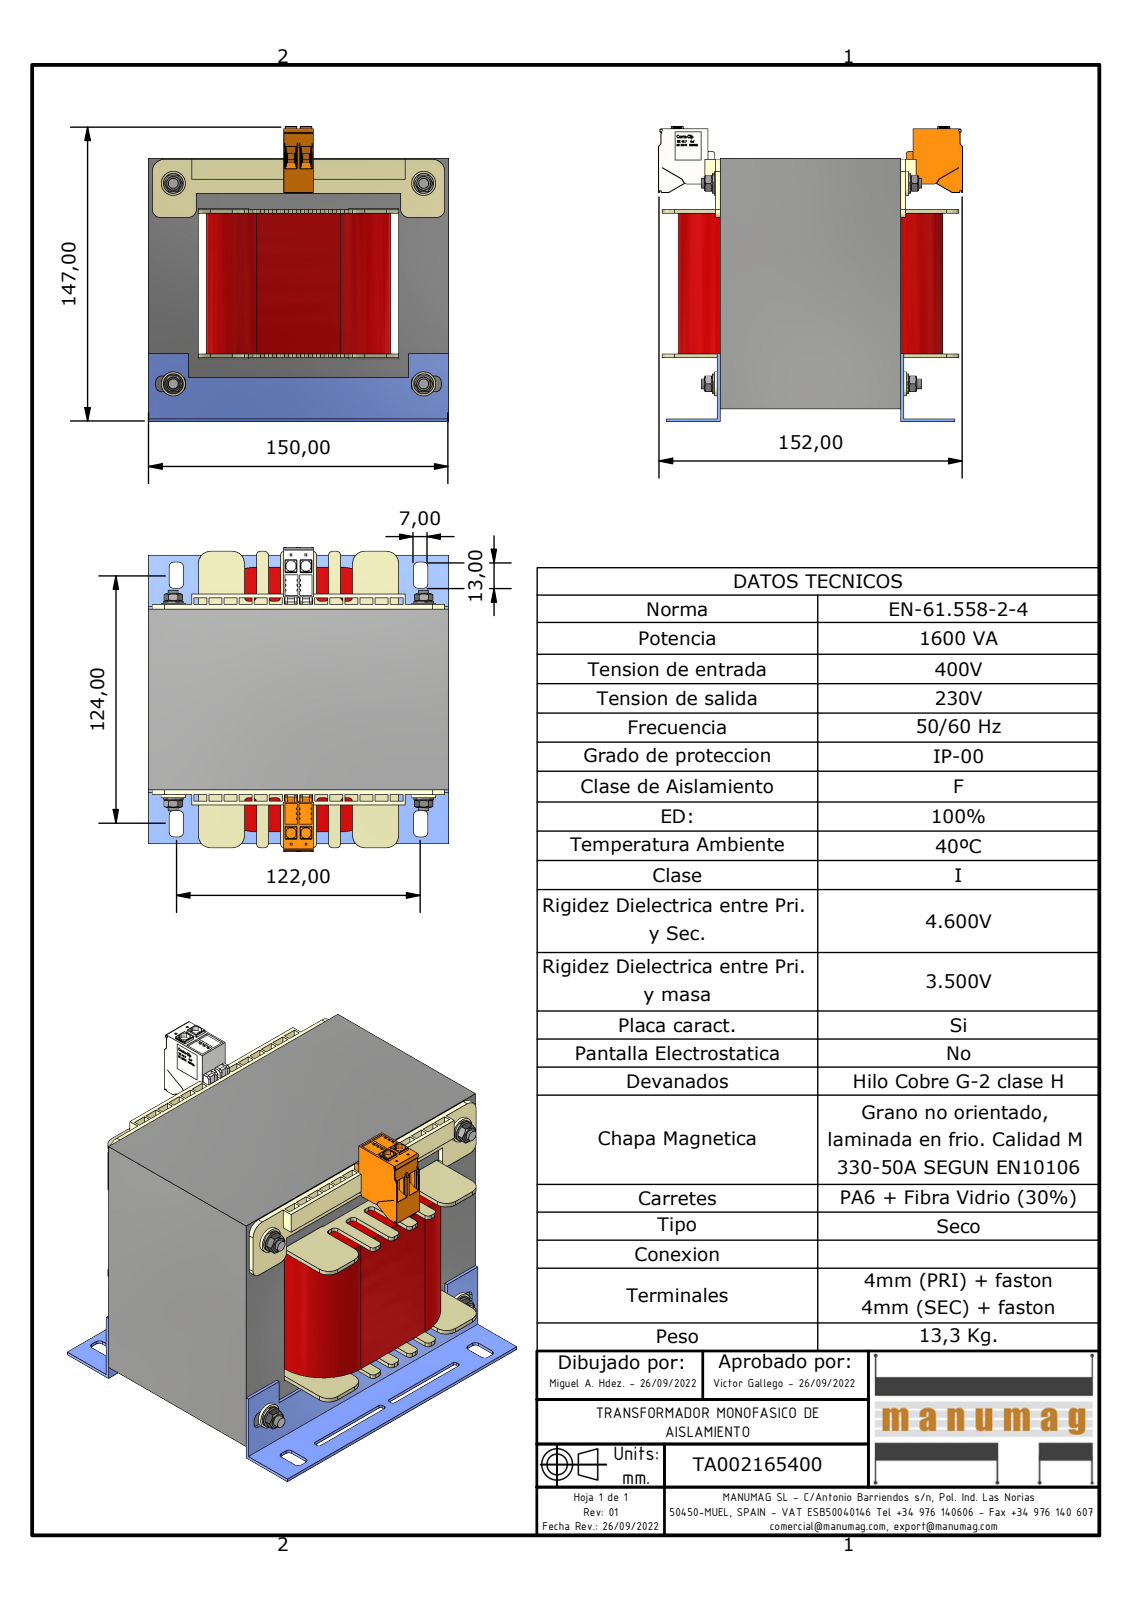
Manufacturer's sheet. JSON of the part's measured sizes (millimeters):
{"part_name": "TA002165400; EI150 x 125 - 90 (RC50); AF50DIN; EI 150 X 125 - 90 (+7 more)", "step_written_by": "Autodesk Inventor 2023 (AUTOMOTIVE_DESIGN)", "units": "millimeters", "bodies": {"solids": 36, "faces": 3990, "planar": 3196, "cylindrical": 566, "other": 228}, "overall_size": [151.9, 150, 147.4], "volume_mm3": 1933000, "surface_area_mm2": 278368, "round_holes": [[4.13, 4], [5, 4], [5.3, 4], [8, 4]], "round_bosses_or_shafts": [[12, 4], [10, 4], [5.9, 4]], "partial_cylinders_radius": [[0.15, 164], [0.2, 60], [2, 52], [1, 24], [0.5, 16], [0.3, 12], [6, 10], [3, 8]], "face_to_face_distances": [25, 100, 50, 125, 90, 75, 99.5, 25.5, 21, 1.5], "hole_center_spacings": [100, 125, 160.08]}
